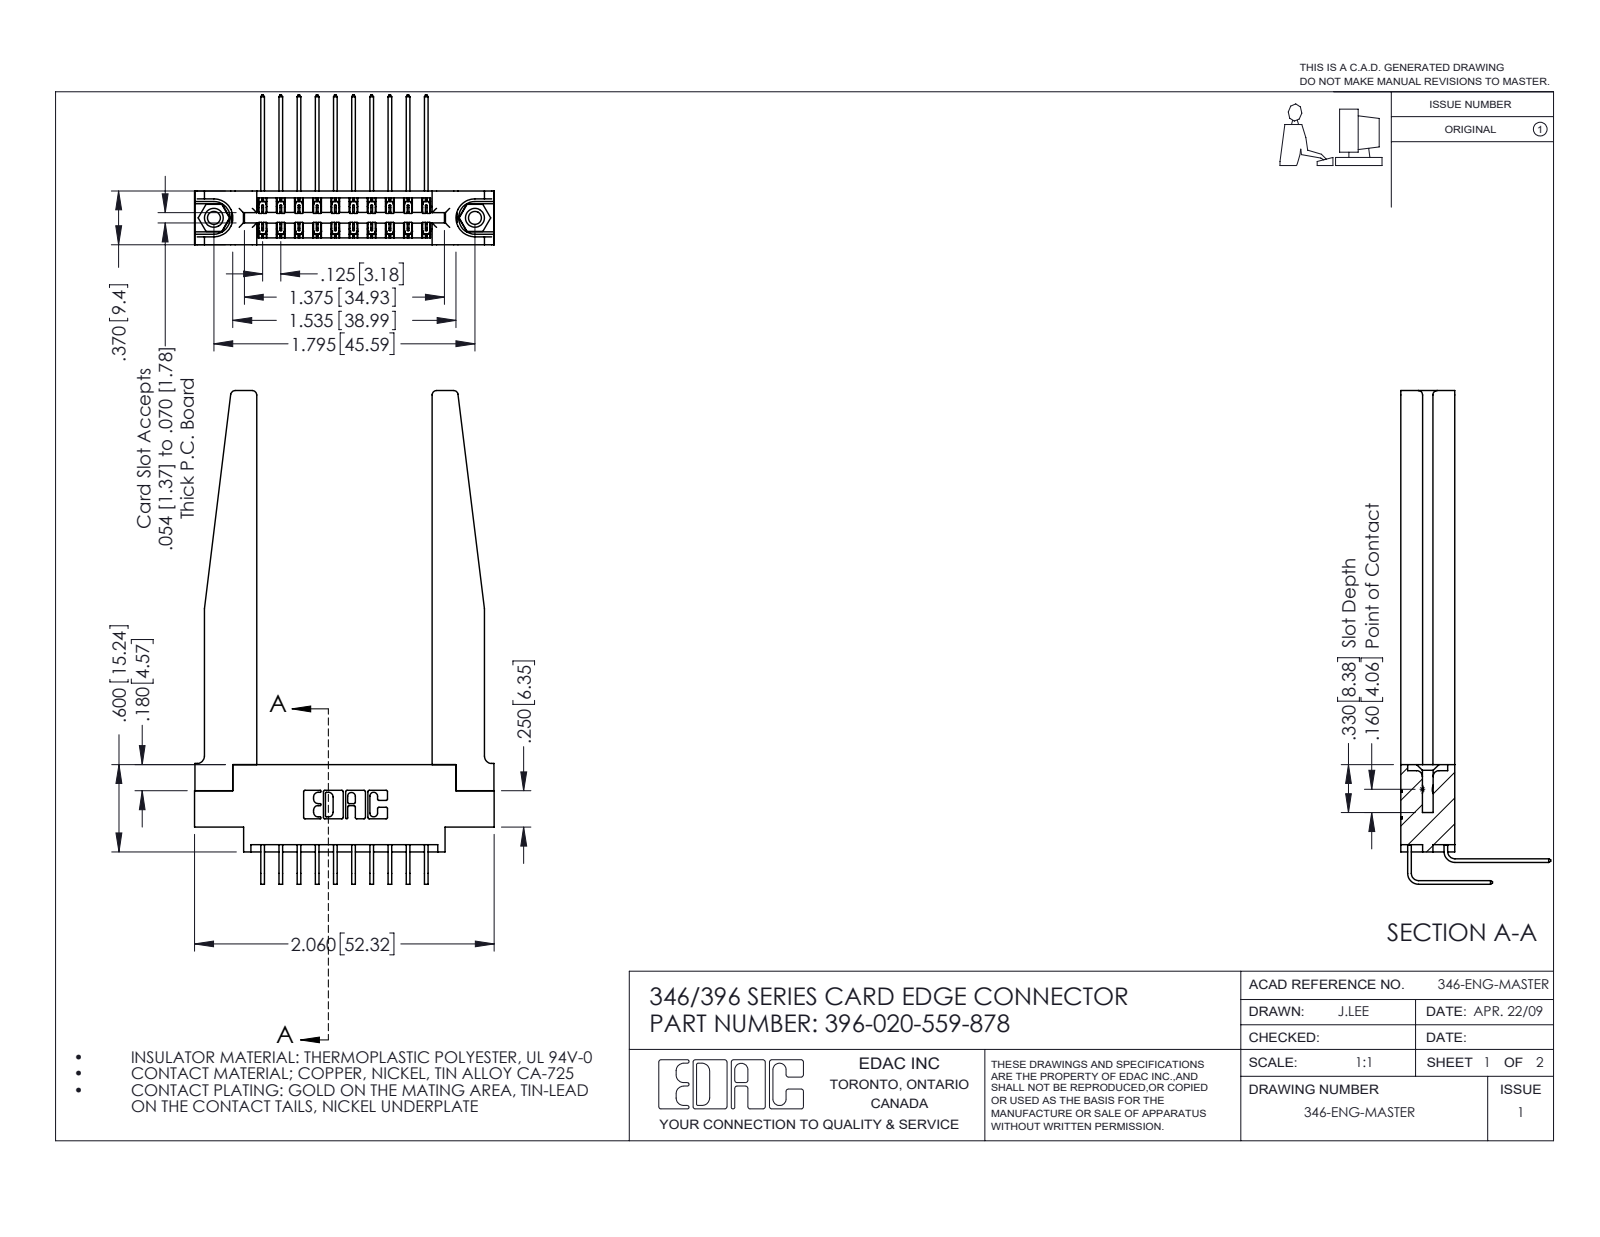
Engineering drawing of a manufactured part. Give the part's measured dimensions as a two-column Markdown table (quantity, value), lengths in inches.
| quantity | value |
| --- | --- |
| part name | 396-020-559-878; 345-250-001_345-250-001-102; 346-220-078_345-220-078; 345-292-001_558 559 Tail - 1 (+2 more) |
| STEP written by | SolidWorks 2016 (CONFIG_CONTROL_DESIGN) |
| units | inches |
| bodies | 25 solids, 1440 faces (962 planar, 426 cylindrical, 52 other) |
| overall size | 3.393 × 2.06 × 1.03 |
| volume | 0.715 in³ |
| surface area | 20.75 in² |
| round holes (diameter × count) | 0.089 × 2, 0.125 × 2, 0.156 × 2, 0.064 × 1 |
| round bosses / shafts (diameter × count) | 0.155 × 2 |
| partial cylindrical surfaces (radius × count) | 0.006 × 30, 0.01 × 22, 0.03 × 8, 0.007 × 6, 0.031 × 6, 0.05 × 4, 0.026 × 3, 0.014 × 2 |
| main face-to-face distances | 0.37, 0.15, 0.072, 0.048, 0.148, 0.322, 0.25, 0.22, 0.102, 0.173 |
| hole center spacings | 0.246, 1.59, 1.795 |
